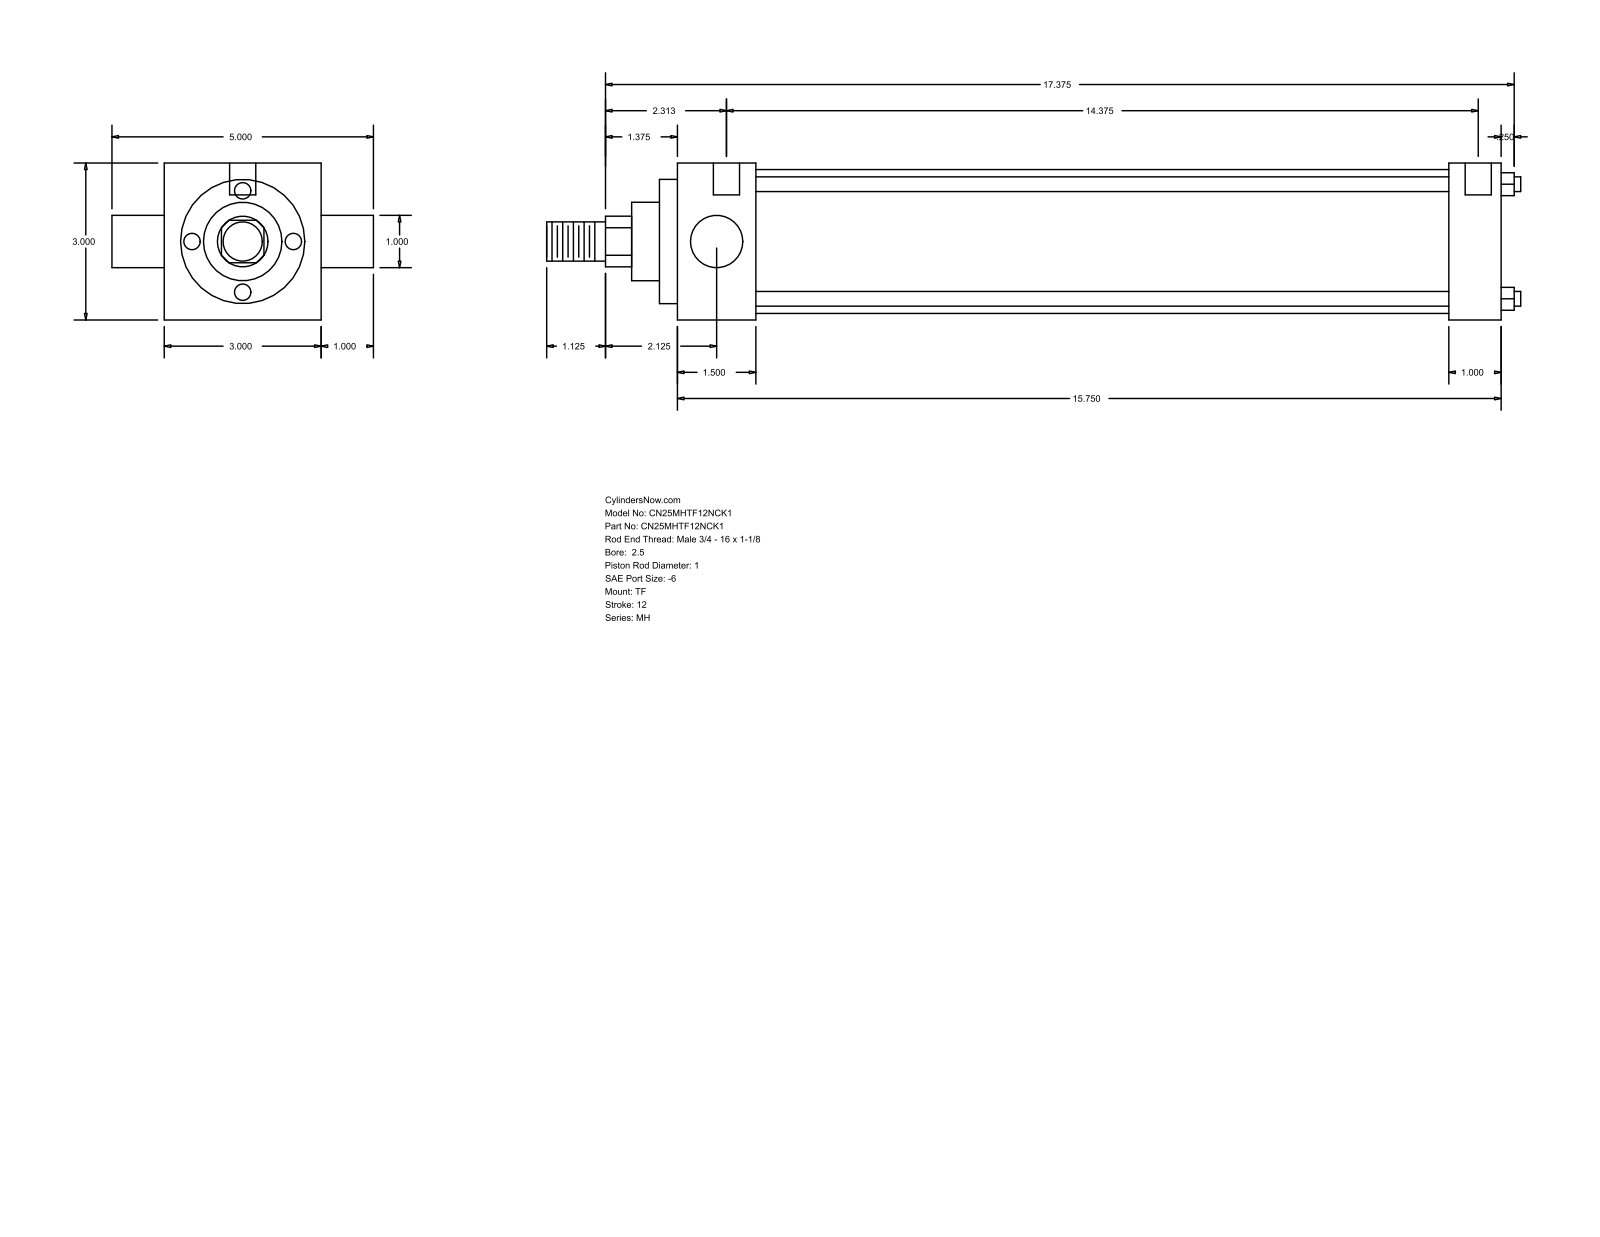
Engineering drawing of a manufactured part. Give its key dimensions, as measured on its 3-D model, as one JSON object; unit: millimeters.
{"part_name": "MH_TF__0250_1", "step_written_by": "GSSL Pune (CONFIG_CONTROL_DESIGN)", "units": "millimeters", "bodies": {"solids": 0, "faces": 86, "planar": 61, "cylindrical": 25, "other": 0}, "overall_size": [473.07, 127, 76.2], "round_holes": [[5.56, 3], [12.7, 2]], "round_bosses_or_shafts": [[7.14, 4], [25.4, 2], [69.85, 1], [60.33, 1], [38.1, 1], [19.05, 1]], "partial_cylinders_radius": [[12.29, 1]], "face_to_face_distances": [76.2, 400.06, 38.11, 361.95, 374.65, 336.54, 25.41, 8.73, 46.84, 383.38], "hole_center_spacings": [3.18, 4.76, 365.12, 368.3, 369.88, 373.06]}
